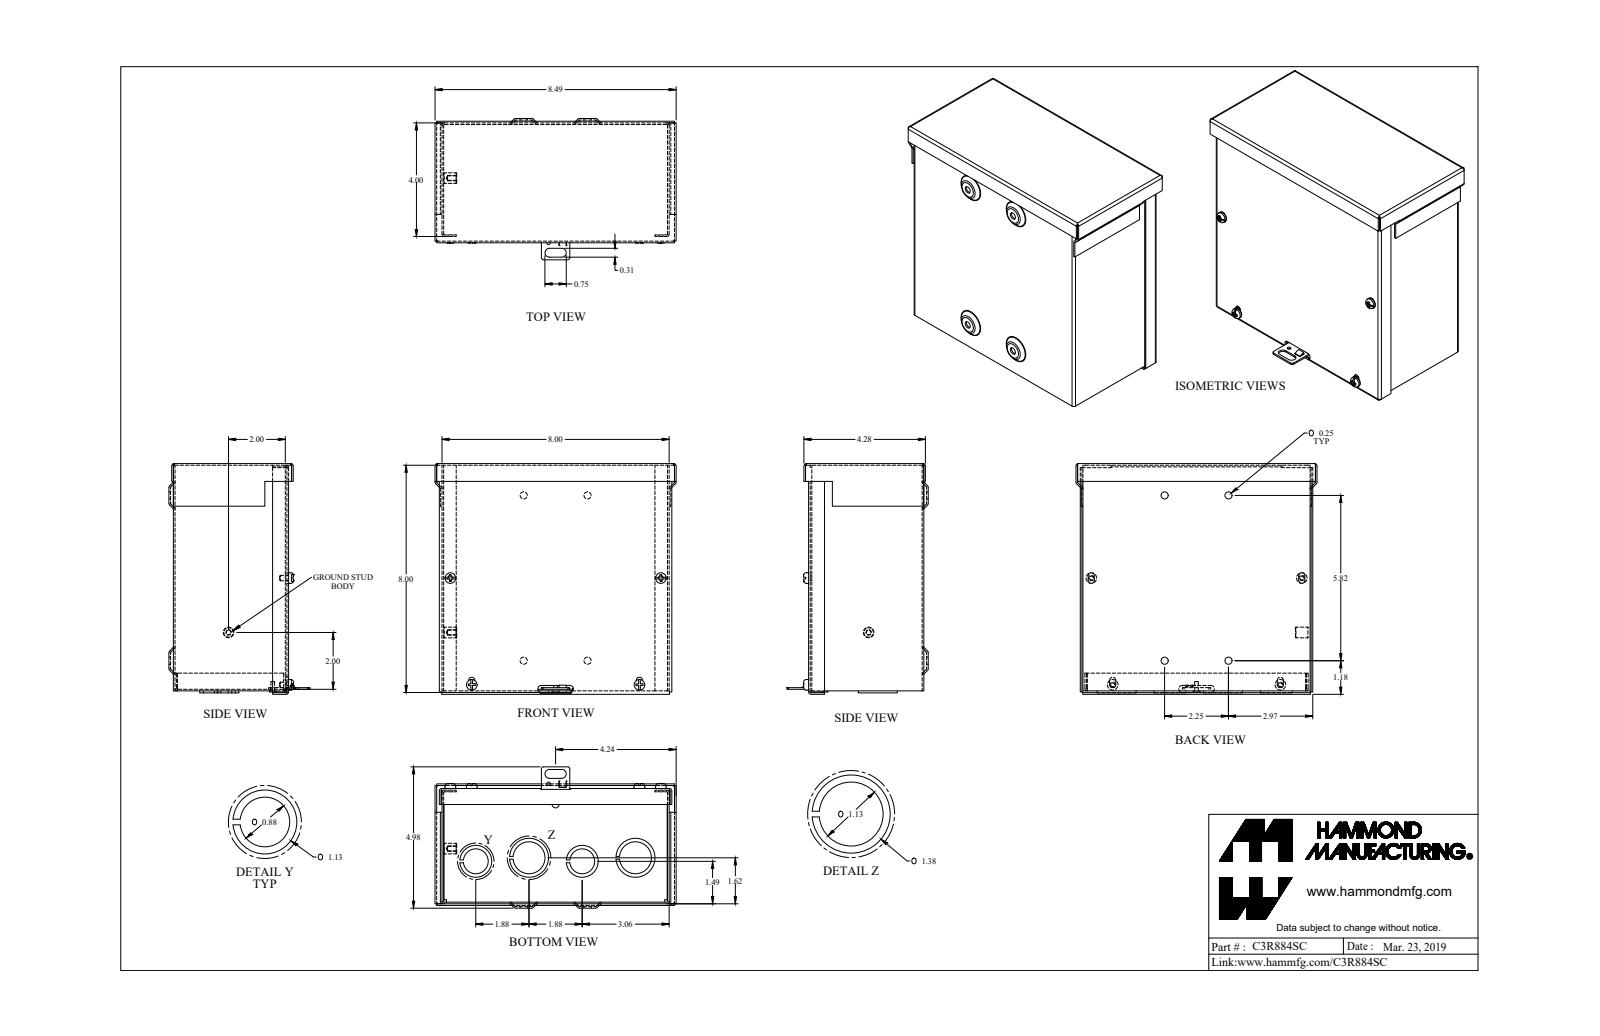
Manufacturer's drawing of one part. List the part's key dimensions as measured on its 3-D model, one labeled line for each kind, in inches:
Part name (STEP PRODUCT): C3R884SC_Default
STEP written by: SolidWorks 2019 (CONFIG_CONTROL_DESIGN)
Units: inches
Bodies: 11 solids, 424 faces (223 planar, 115 cylindrical, 86 other)
Overall size (bounding box): 8.489 × 8.12 × 4.977
Volume: 17.99 in³ · Surface area: 637.2 in²
Round holes (diameter × count): ⌀0.17 ×4, ⌀0.25 ×4, ⌀1.125 ×2, ⌀0.125 ×1, ⌀0.137 ×1, ⌀0.156 ×1, ⌀0.875 ×1, ⌀0.875 ×1
Round bosses / shafts (diameter × count): ⌀0.375 ×4, ⌀0.19 ×4, ⌀1.375 ×2, ⌀1.125 ×2, ⌀0.375 ×1, ⌀0.125 ×1
Partial cylindrical surfaces — rounded edges, fillets, slot ends (radius × count): R0.029 ×21, R0.086 ×21, R0.109 ×8, R0.125 ×8, R0.156 ×2
Main face-to-face distances: 0.057, 4, 7.943, 3.943, 4.057, 8, 0.057, 7.886, 7.886, 7.943
Hole centre spacings: 3.89, 5.64, 1.88, 1.998, 2.25, 3.75, 3.752, 4.165
